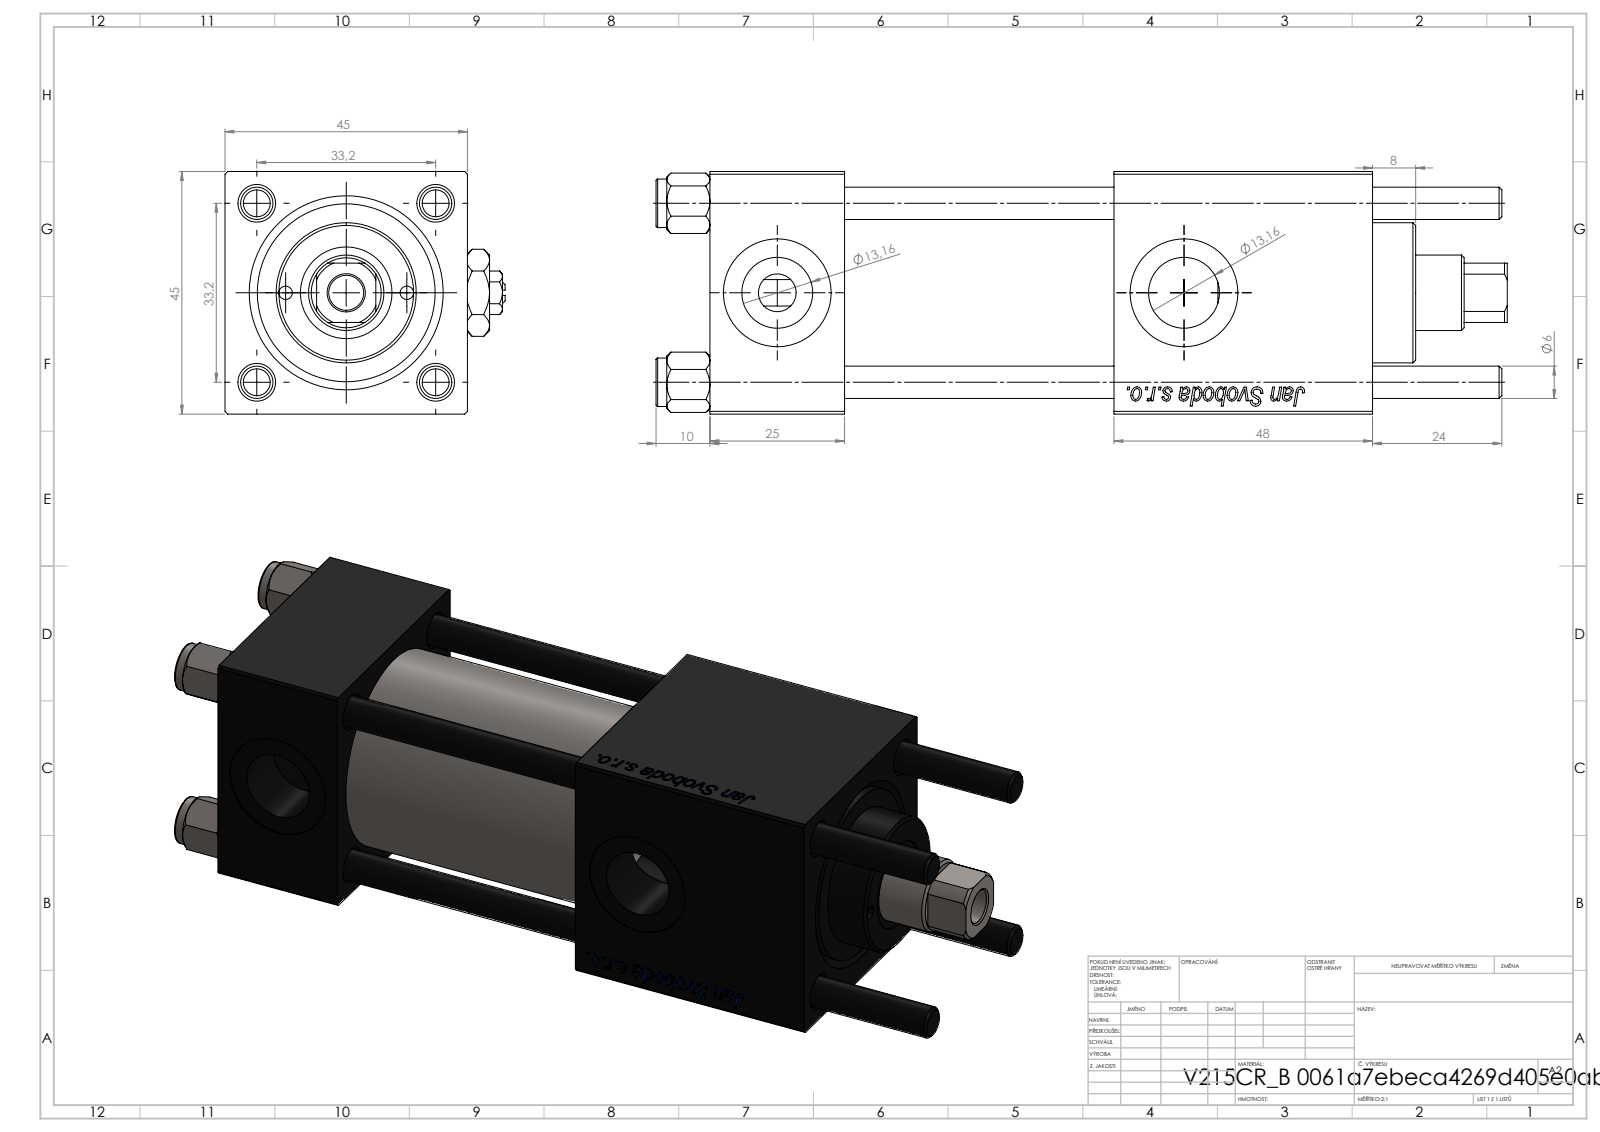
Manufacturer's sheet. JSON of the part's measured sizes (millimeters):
{"part_name": "V215CR_VCP_B; Zatka_pro_OIL_PORT; V215_VC_A; NUT_M5_B (+2 more)", "step_written_by": "SolidWorks 2019 (CONFIG_CONTROL_DESIGN)", "units": "millimeters", "bodies": {"solids": 12, "faces": 1214, "planar": 456, "cylindrical": 88, "other": 670}, "overall_size": [158, 52, 45], "volume_mm3": 197395, "surface_area_mm2": 73855, "round_holes": [[6, 4], [2.5, 2], [7, 2], [13.16, 2], [20, 2], [6.5, 1], [14, 1], [17, 1], [24, 1], [32, 1], [33, 1]], "round_bosses_or_shafts": [[9, 4], [38, 1], [26, 1]], "partial_cylinders_radius": [[6.5, 1]], "face_to_face_distances": [45, 25, 123, 98, 50, 75, 48, 94.3, 69.3, 19.3], "hole_center_spacings": [17.44, 23.48, 32.42, 33.2, 11.25, 46.95, 22.5, 75.5]}
